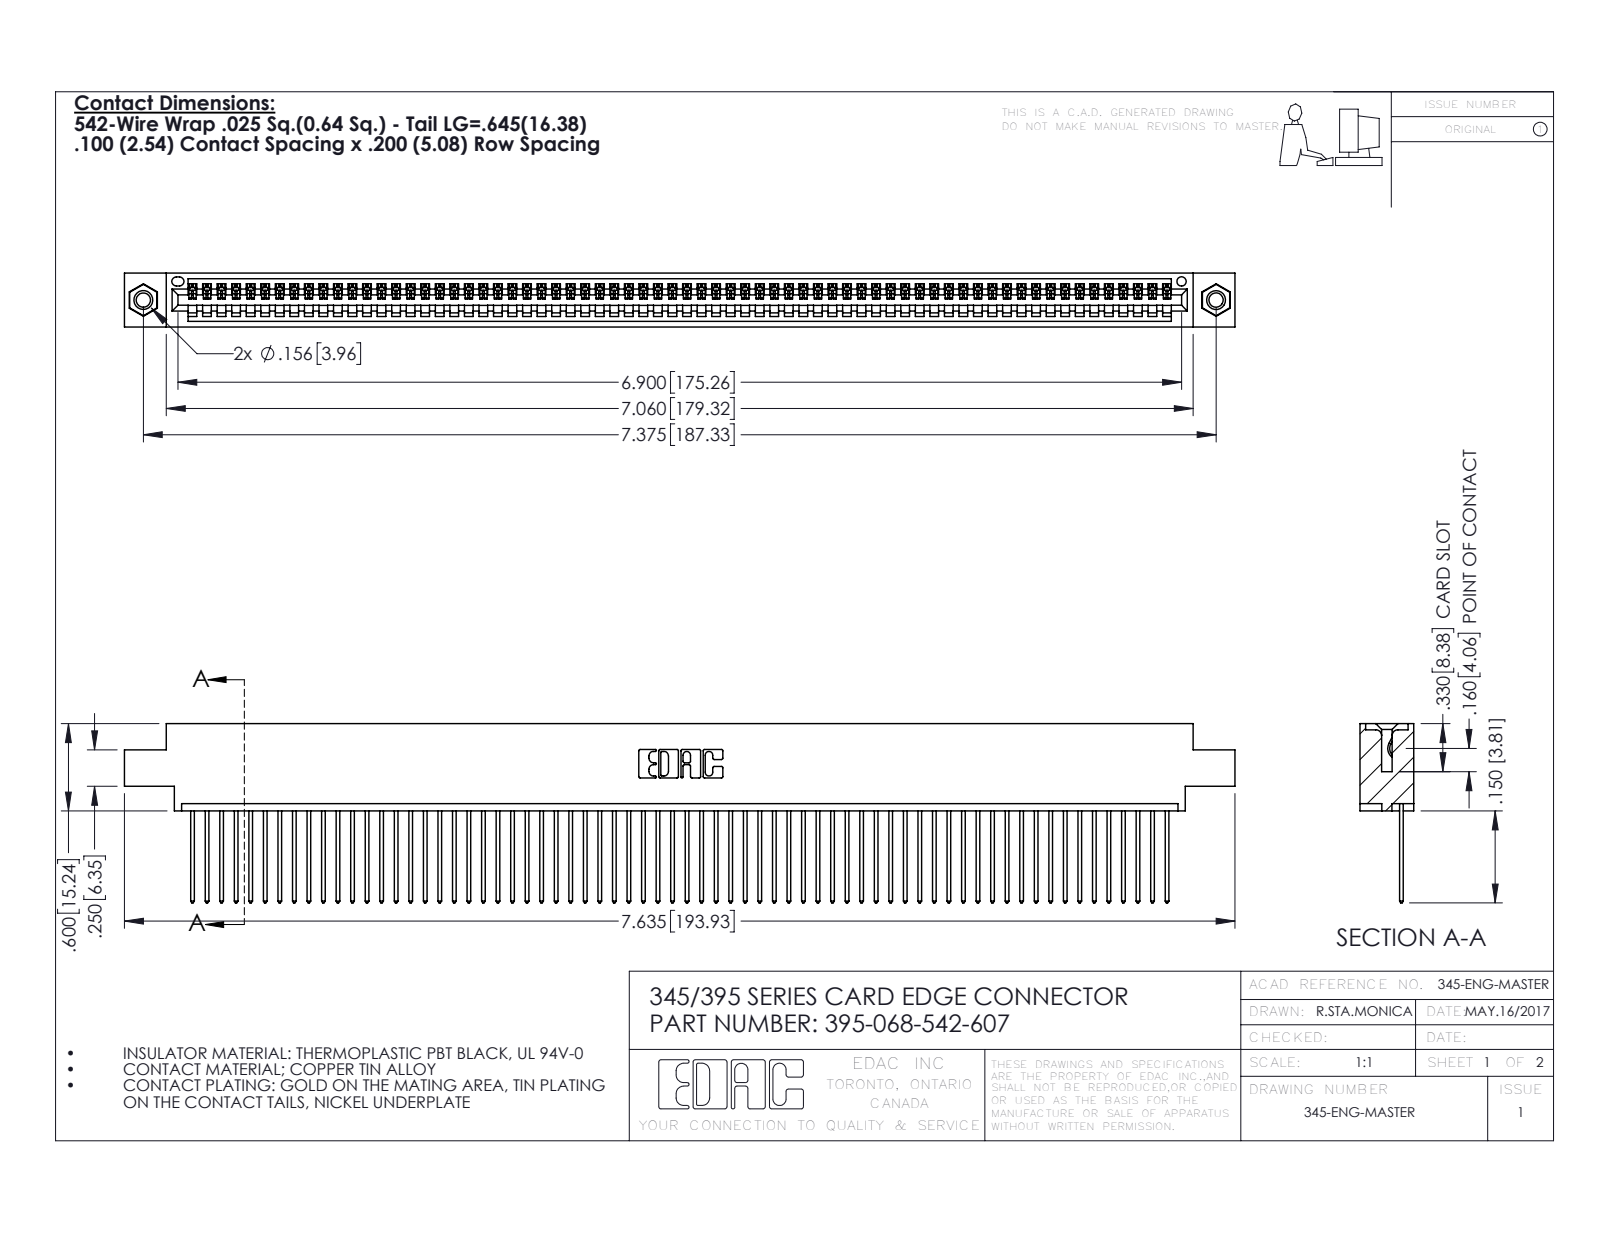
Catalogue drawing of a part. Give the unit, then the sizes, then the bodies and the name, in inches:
Units: inches
Overall size (bounding box): 7.635 × 1.232 × 0.37
Round holes (diameter × count): ⌀0.098 ×2, ⌀0.125 ×2, ⌀0.156 ×2, ⌀0.064 ×1
Round bosses / shafts (diameter × count): ⌀0.155 ×2
Partial cylindrical surfaces — rounded edges, fillets, slot ends (radius × count): R0.006 ×136, R0.01 ×136, R0.01 ×22, R0.007 ×6, R0.031 ×6, R0.026 ×3, R0.031 ×2, R0.04 ×2
Main face-to-face distances: 0.072, 0.298, 0.37, 0.098, 0.272, 0.025, 0.2, 0.225, 0.175, 0.149
Hole centre spacings: 0.27, 7.139, 7.375
Volume: 1.139 in³ · Surface area: 40.71 in²
Bodies: 71 solids, 4134 faces (2836 planar, 1282 cylindrical, 16 other)
Part name (STEP PRODUCT): 345-250-001_345-250-005-103; 345 Part_0.170 Offset - 0.156 Dia-TI; 345-292-001_345-293-142; 395-068-542-607
STEP written by: SolidWorks 2016 (CONFIG_CONTROL_DESIGN)
